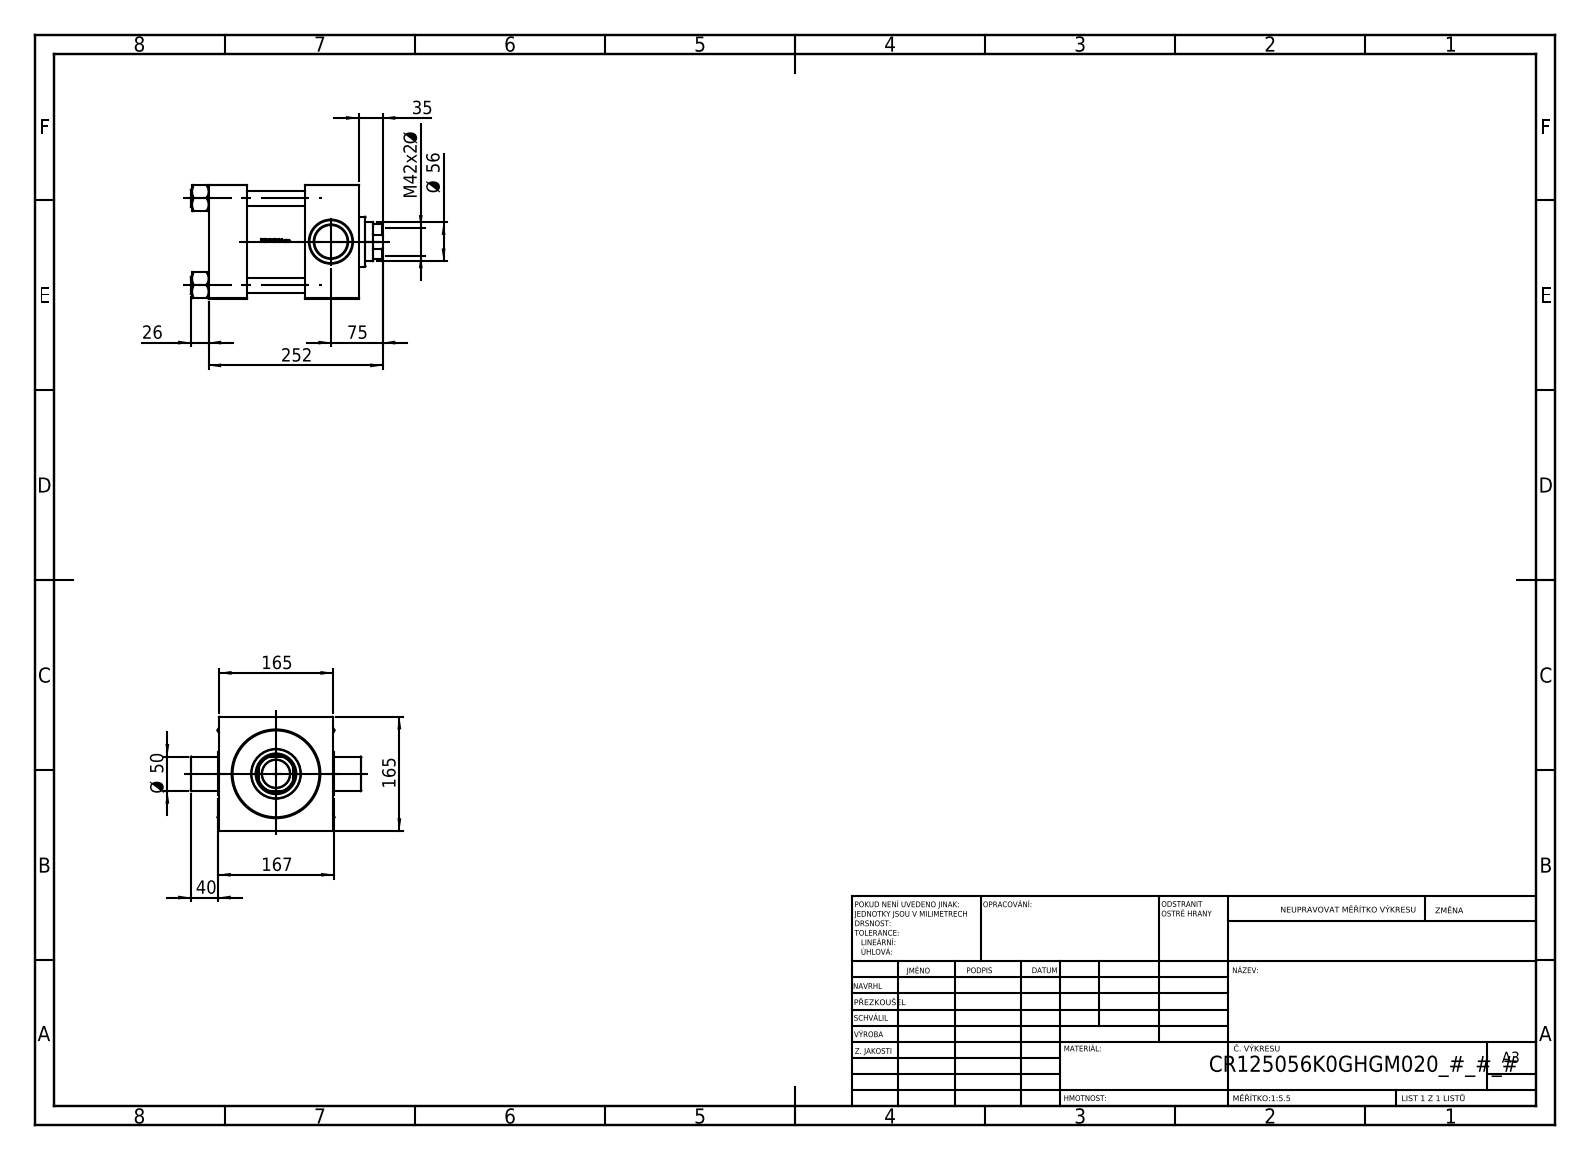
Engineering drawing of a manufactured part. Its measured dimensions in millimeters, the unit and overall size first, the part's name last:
Units: millimetres
Overall size (bounding box): 278 × 247 × 165
Round holes (diameter × count): ⌀22 ×4, ⌀7 ×1, ⌀40.5 ×1, ⌀56 ×1, ⌀59 ×1, ⌀96 ×1, ⌀125 ×1, ⌀125.5 ×1
Round bosses / shafts (diameter × count): ⌀25 ×4, ⌀131 ×1, ⌀72 ×1, ⌀50 ×1
Partial cylindrical surfaces — rounded edges, fillets, slot ends (radius × count): R27 ×1
Main face-to-face distances: 165, 55, 217, 162, 139, 84, 78, 64, 98, 119
Hole centre spacings: 89.02, 125.9, 178.05
Volume: 4 724 000 mm³ · Surface area: 501 639 mm²
Bodies: 11 solids, 1107 faces (475 planar, 110 cylindrical, 522 other)
Part name (STEP PRODUCT): V215CR_VCP_K; V215_VC_A; V215CR_K_TYCINKA; V215CR_K_Body (+1 more)
STEP written by: SolidWorks 2019 (CONFIG_CONTROL_DESIGN)
